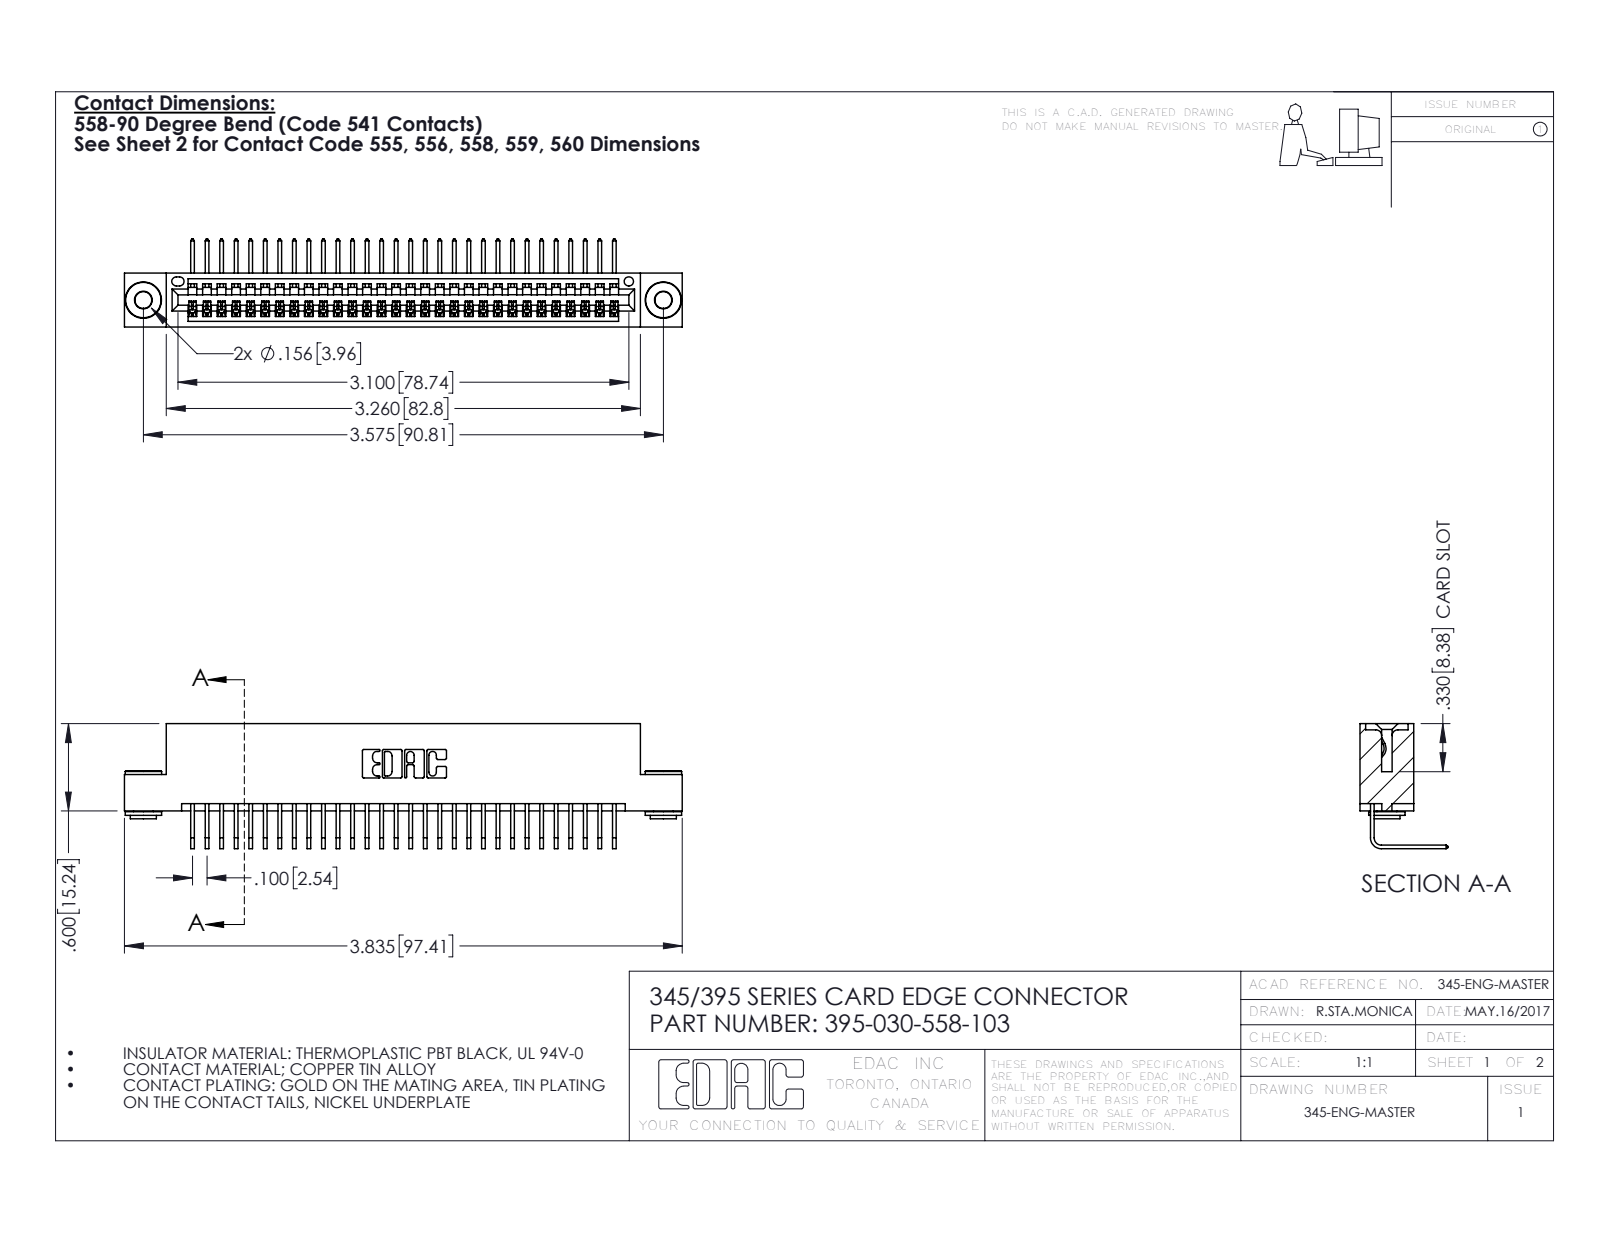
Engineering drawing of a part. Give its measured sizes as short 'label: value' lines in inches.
name: 345 Part_Flush Mounting Lugs - 0.156 Dia-TH; 345-250-002_345-250-002-102; 395-030-558-103; 345-292-001_558 Tail - 2
written by: SolidWorks 2016 (CONFIG_CONTROL_DESIGN)
unit: in
bodies: 33 solids, 1964 faces (1350 planar, 606 cylindrical, 8 other)
size: 3.835 × 0.859 × 0.605
volume: 0.566 in³; area: 20.09 in²
holes: 2× ⌀0.116, 2× ⌀0.156, 1× ⌀0.064
bosses: 2× ⌀0.25, 2× ⌀0.18, 2× ⌀0.136
rounds: 60× R0.006, 22× R0.01, 6× R0.007, 6× R0.031, 3× R0.026, 2× R0.031, 2× R0.04, 1× R0.014
face distances: 0.072, 0.298, 0.2, 0.37, 0.025, 0.098, 0.272, 0.225, 0.149, 0.072
hole spacings: 0.27, 3.34, 3.575
